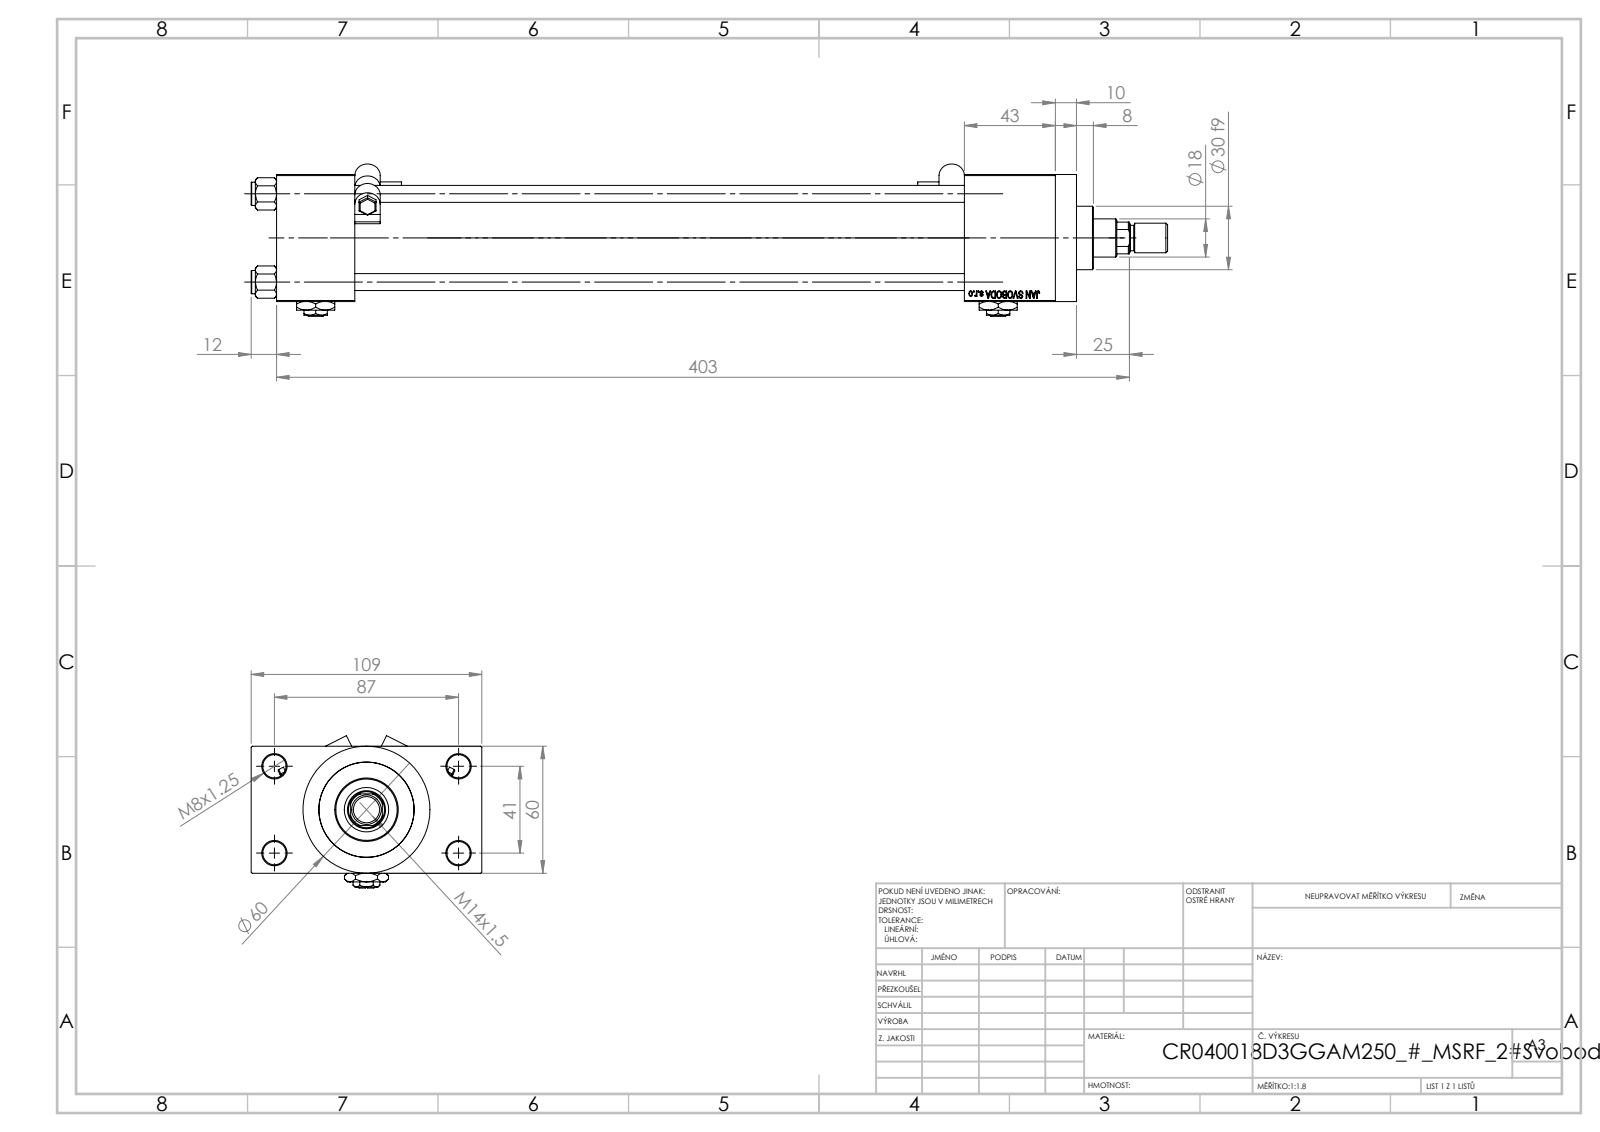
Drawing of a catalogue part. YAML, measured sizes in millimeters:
part_name: "V215_VC_A; MSRF_MSRG1; ROD_END_AH; V215CR_D_TYCINKA (+4 more)"
step_written_by: "SolidWorks 2019 (CONFIG_CONTROL_DESIGN)"
units: millimeters
bodies: {solids: 16, faces: 1284, planar: 586, cylindrical: 132, other: 566}
overall_size: [433, 109, 71.97]
volume: 723321
surface_area: 227603
round_holes:
  - {diameter: 8, count: 4}
  - {diameter: 11, count: 4}
  - {diameter: 7, count: 2}
  - {diameter: 16.66, count: 2}
  - {diameter: 24, count: 2}
  - {diameter: 8.5, count: 1}
  - {diameter: 18, count: 1}
  - {diameter: 21, count: 1}
  - {diameter: 31, count: 1}
  - {diameter: 40, count: 1}
  - {diameter: 45, count: 1}
round_bosses_or_shafts:
  - {diameter: 11, count: 4}
  - {diameter: 5, count: 2}
  - {diameter: 2.5, count: 2}
  - {diameter: 60, count: 1}
  - {diameter: 46, count: 1}
  - {diameter: 30, count: 1}
  - {diameter: 14, count: 1}
  - {diameter: 12, count: 1}
partial_cylinders:
  - {radius: 0.5, count: 12}
  - {radius: 6, count: 4}
  - {radius: 8.5, count: 1}
face_to_face_distances: [60, 24.5, 84.5, 288, 325, 37, 43, 368, 331, 109]
hole_center_spacings: [22.65, 29.49, 41.7, 47.15, 48.09, 64.35, 76.49, 41]
